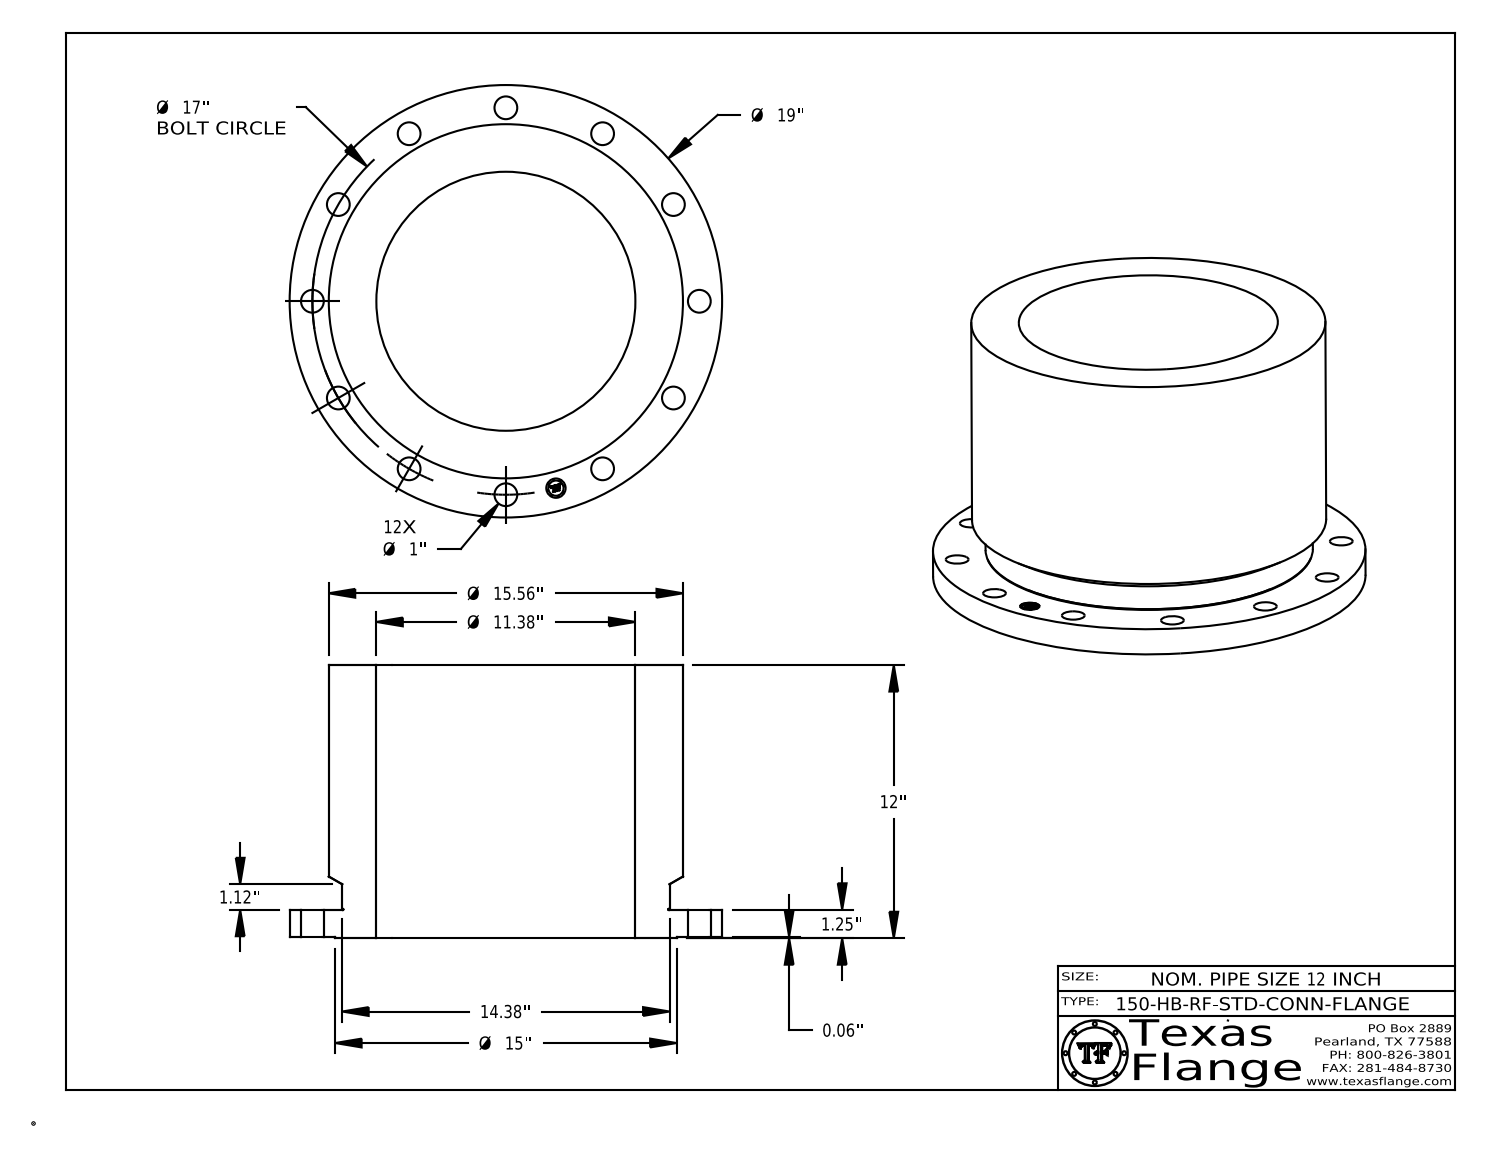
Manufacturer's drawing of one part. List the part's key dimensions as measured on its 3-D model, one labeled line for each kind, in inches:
Part name (STEP PRODUCT): 12-150-HB-RF-STD-CONN-FLANGE
STEP written by: CATIA V5 STEP AP214 (AUTOMOTIVE_DESIGN)
Units: inches
Bodies: 1 solid, 429 faces (369 planar, 54 cylindrical, 6 other)
Overall size (bounding box): 19 × 19 × 12
Volume: 1 124 in³ · Surface area: 1 459 in²
Round holes (diameter × count): ⌀1 ×12, ⌀0.85 ×1, ⌀11.38 ×1
Round bosses / shafts (diameter × count): ⌀0.051 ×8, ⌀19 ×1, ⌀15.56 ×1, ⌀15 ×1, ⌀14.38 ×1, ⌀0.67 ×1
Main face-to-face distances: 1.187, 11.937, 10.75, 0.063, 1.25, 12, 1.245, 1.183, 10.755, 0.254
Hole centre spacings: 8.5, 16.42, 4.4, 12.02, 14.722, 4.4, 12.021, 14.722
